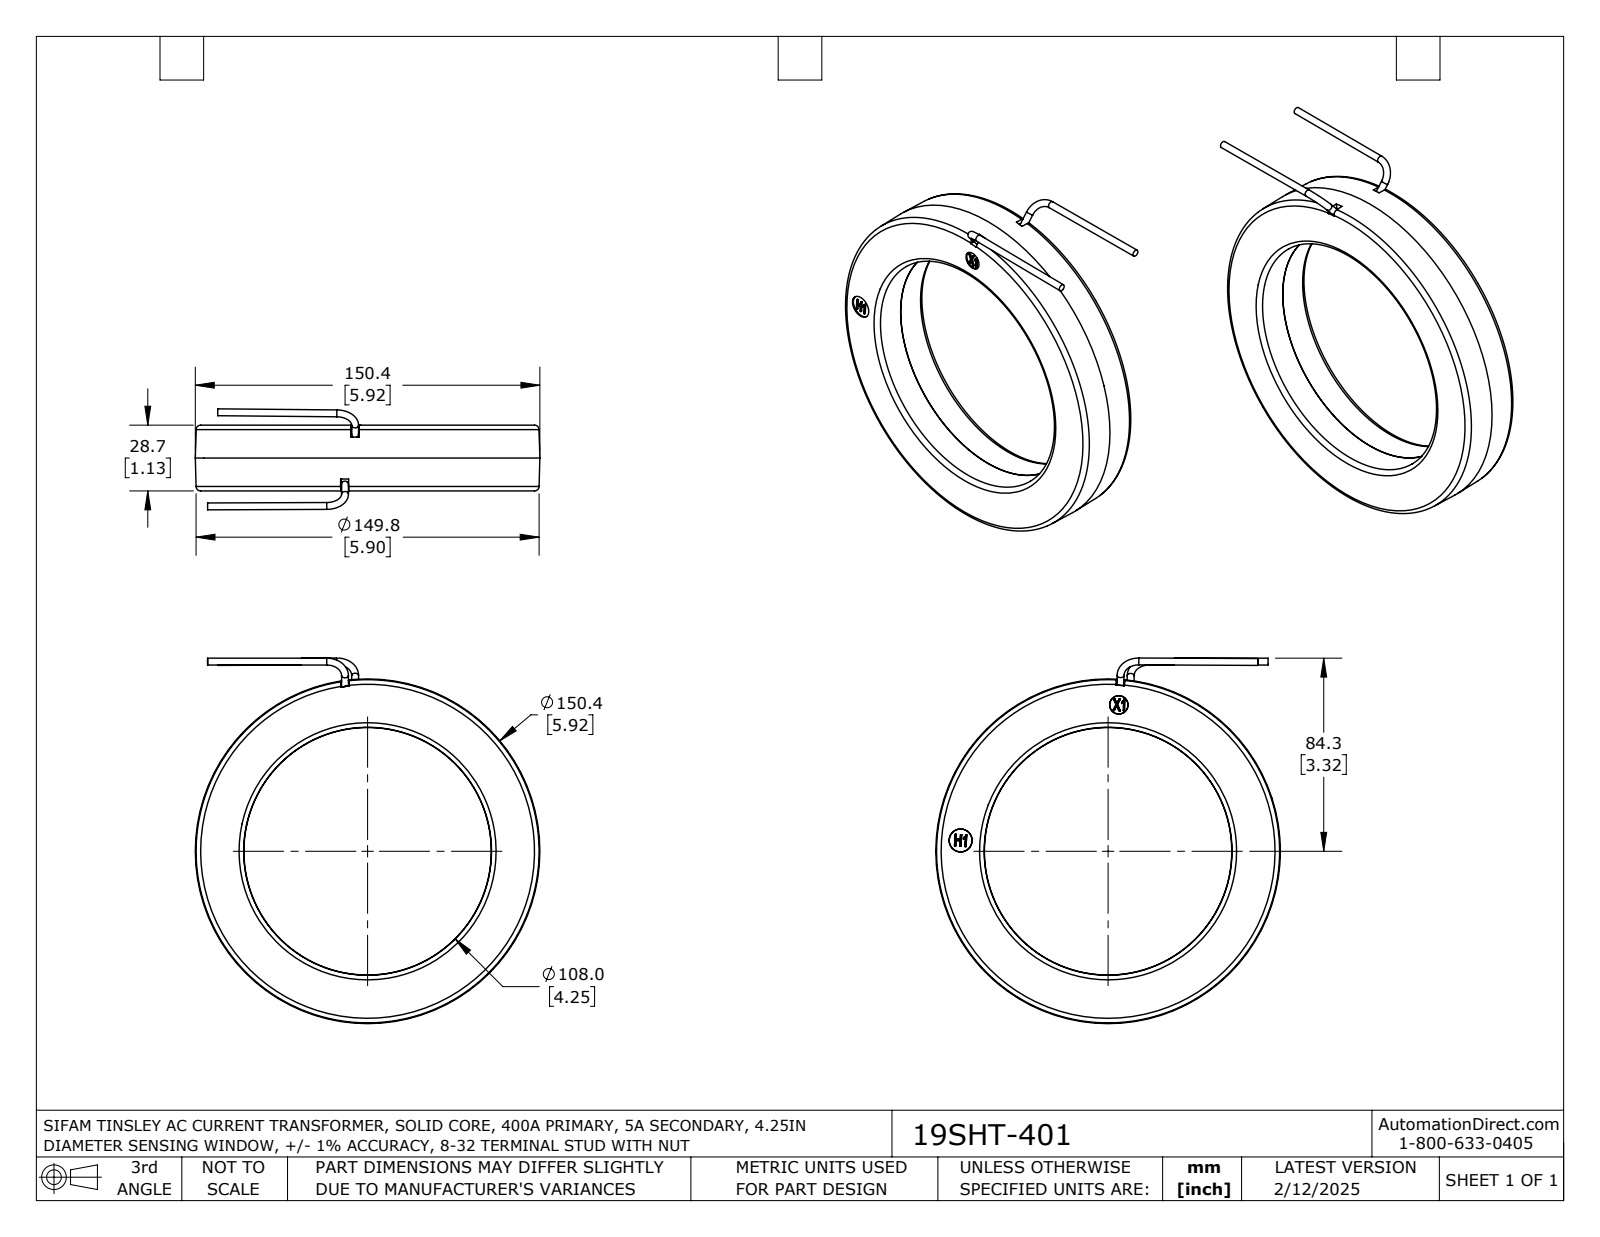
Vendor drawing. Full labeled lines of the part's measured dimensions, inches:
Part name (STEP PRODUCT): 19SHT-401
STEP written by: SolidWorks 2021 (AUTOMOTIVE_DESIGN)
Units: inches
Bodies: 1 solid, 412 faces (248 planar, 78 cylindrical, 86 other)
Overall size (bounding box): 6.611 × 6 × 2.909
Volume: 25.87 in³ · Surface area: 162.8 in²
Round bosses / shafts (diameter × count): ⌀0.394 ×2, ⌀0.236 ×2, ⌀0.217 ×2, ⌀0.158 ×2
Partial cylindrical surfaces — rounded edges, fillets, slot ends (radius × count): R0.11 ×12, R0.039 ×8, R0.098 ×8, R0.138 ×4, R0.012 ×2, R0.051 ×2, R0.054 ×2
Main face-to-face distances: 0.577, 0.573, 0.039, 1.15, 0.612, 0.616, 1.189, 6, 1.228, 6.17
